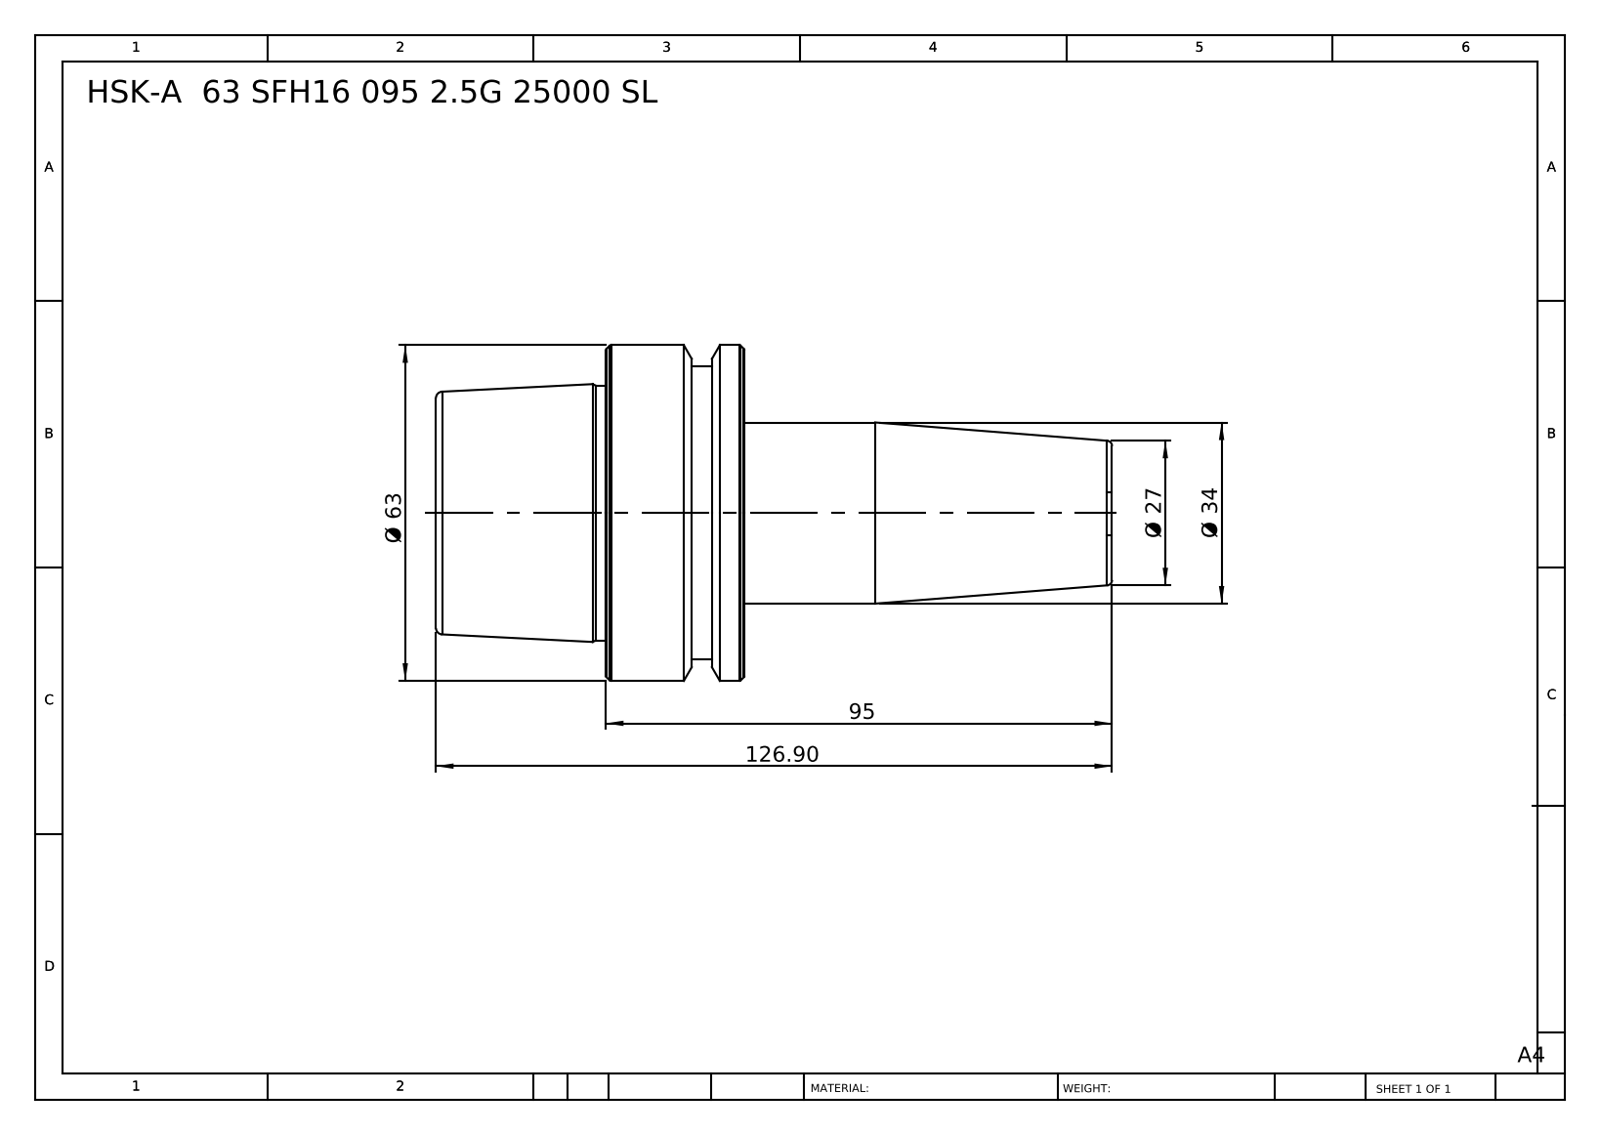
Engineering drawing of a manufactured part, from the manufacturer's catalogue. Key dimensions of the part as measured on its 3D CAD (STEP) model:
Part name (STEP PRODUCT): HSK-A 63 SFH16 095 2.5G 25000 SL
STEP written by: SolidWorks 2014 (CONFIG_CONTROL_DESIGN)
Units: millimetres
Bodies: 1 solid, 46 faces (6 planar, 10 cylindrical, 30 other)
Overall size (bounding box): 126.9 × 63 × 63
Volume: 187 485 mm³ · Surface area: 23 177 mm²
Round bosses / shafts (diameter × count): ⌀63 ×1, ⌀55 ×1, ⌀47.78 ×1, ⌀34 ×1
Main face-to-face distances: 57.9, 26, 31.9, 69, 95, 126.9, 75.1, 6.1, 19.9, 51.8
